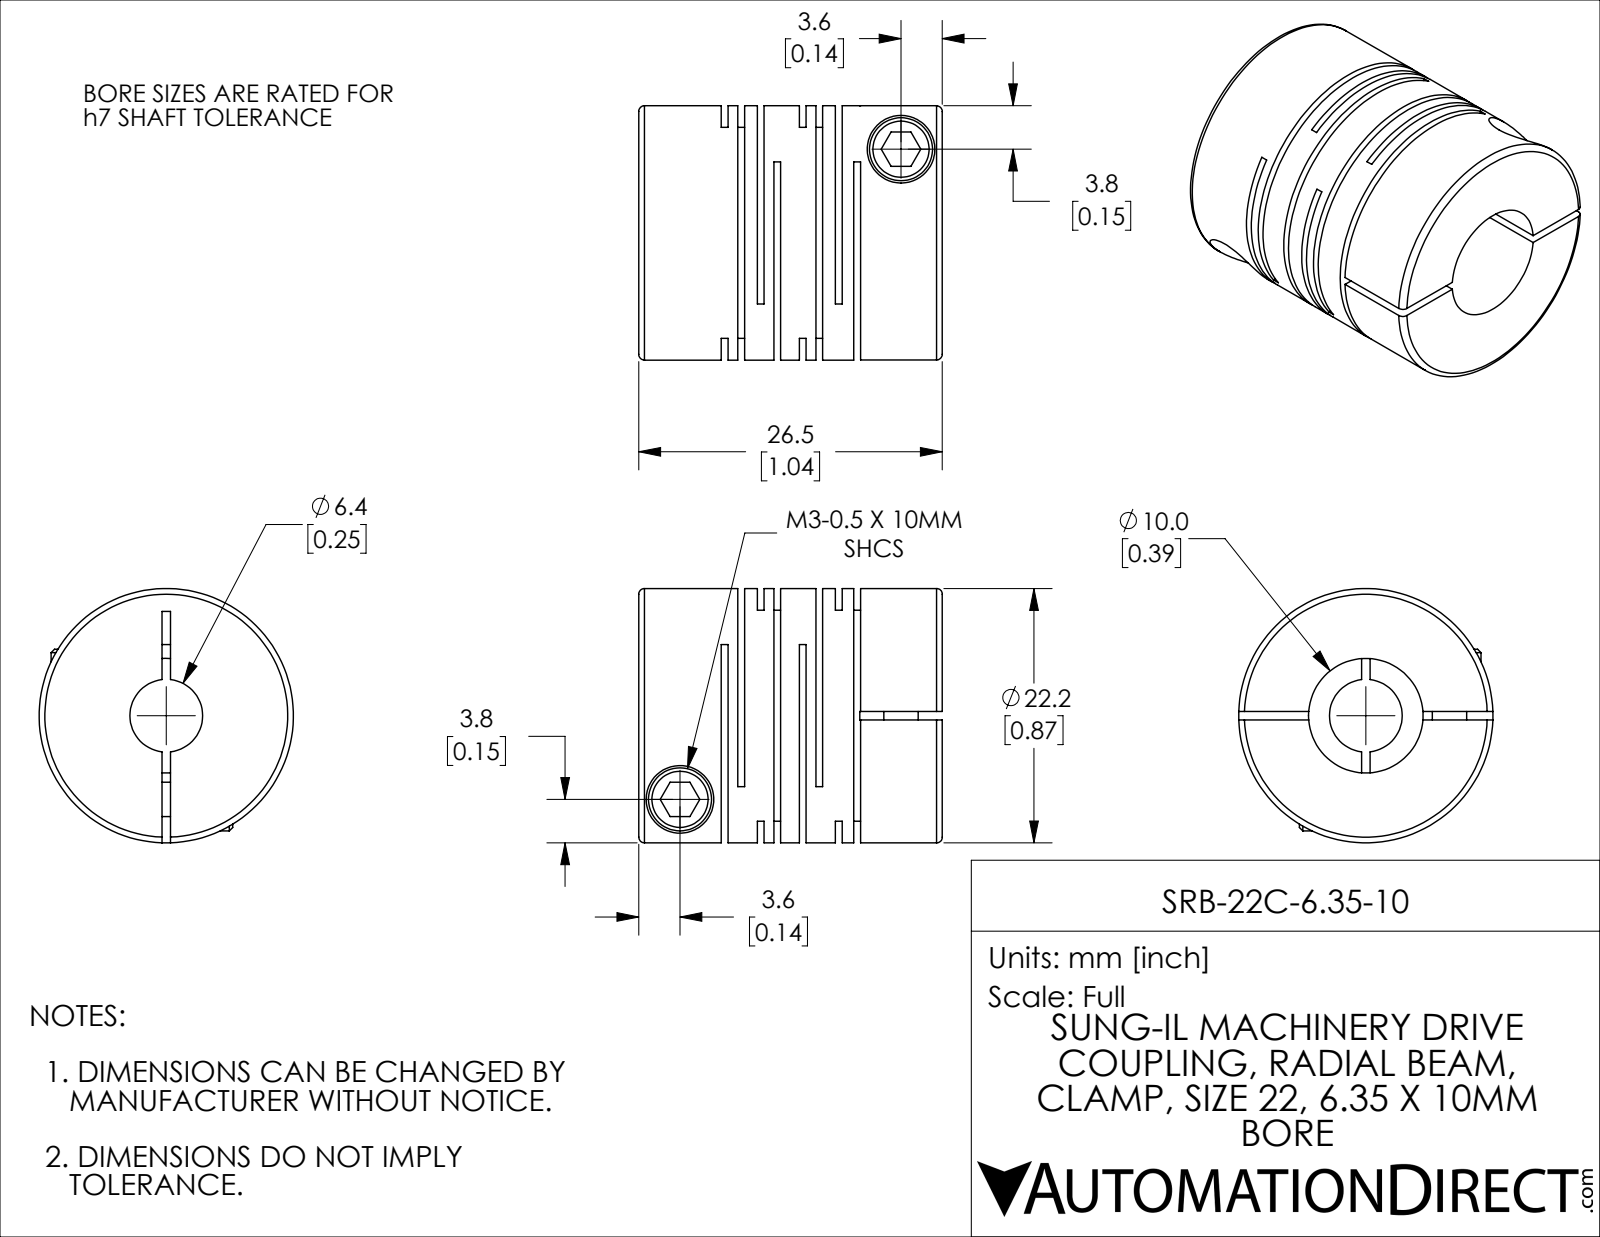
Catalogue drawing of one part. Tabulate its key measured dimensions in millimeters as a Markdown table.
| quantity | value |
| --- | --- |
| part name | SRB-22C-6.35-10 |
| STEP written by | SolidWorks 2021 (CONFIG_CONTROL_DESIGN) |
| units | millimeters |
| bodies | 1 solid, 115 faces (60 planar, 42 cylindrical, 13 other) |
| overall size | 26.5 × 22.2 × 22.2 |
| volume | 7 034 mm³ |
| surface area | 7 494 mm² |
| round holes (diameter × count) | 3 × 2, 5.9 × 2, 6.35 × 1, 10 × 1 |
| round bosses / shafts (diameter × count) | 5.5 × 2, 22.2 × 1 |
| main face-to-face distances | 0.59, 3.15, 6.82, 1.45, 5.37, 3.67, 1.7, 2.04, 3.74, 7.41 |
